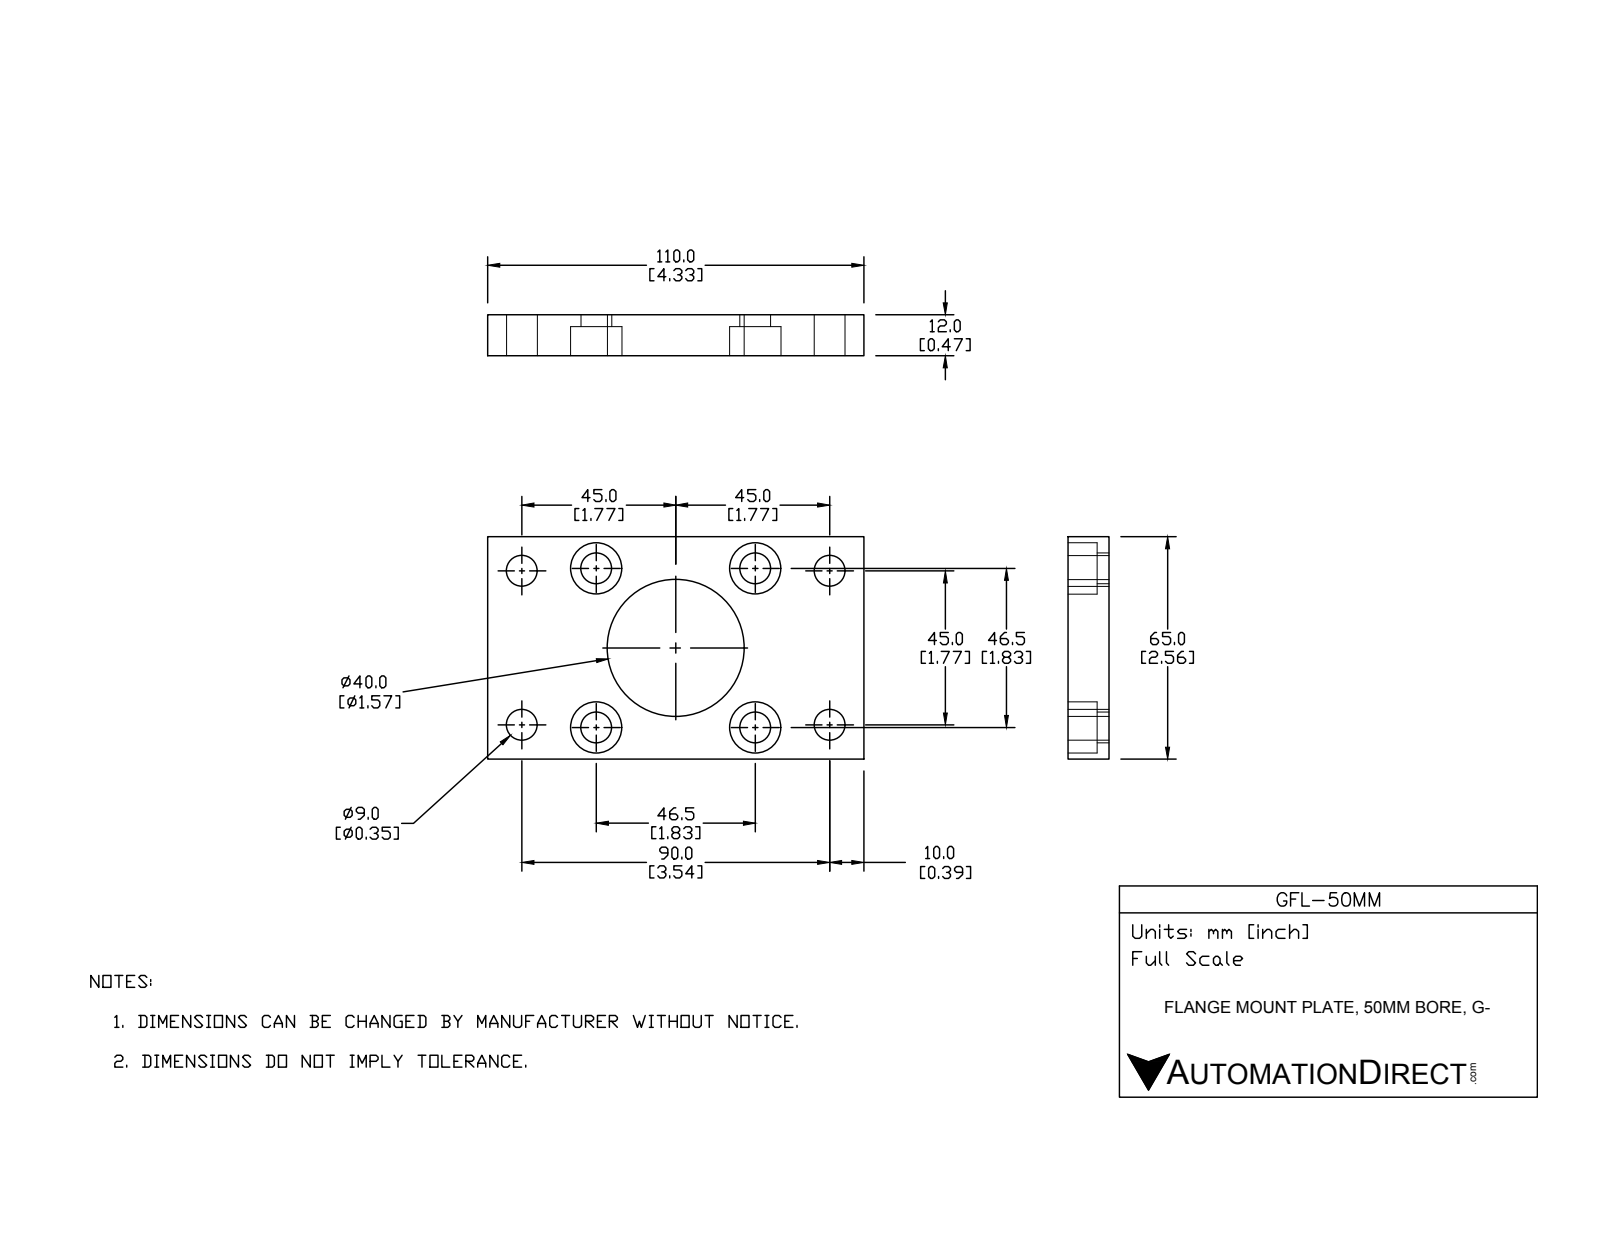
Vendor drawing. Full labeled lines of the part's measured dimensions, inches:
Part name (STEP PRODUCT): GFL-50MM
STEP written by: SolidWorks 2017 (AUTOMOTIVE_DESIGN)
Units: inches
Bodies: 1 solid, 36 faces (10 planar, 26 cylindrical, 0 other)
Overall size (bounding box): 4.331 × 2.559 × 0.472
Volume: 3.708 in³ · Surface area: 30.74 in²
Round holes (diameter × count): ⌀0.354 ×8, ⌀0.591 ×4, ⌀1.575 ×1
Main face-to-face distances: 0.472, 2.559, 4.331, 0.138, 0.335
Hole centre spacings: 0.857, 1.294, 1.831, 1.981, 1.994, 2.687, 3.235, 1.772
